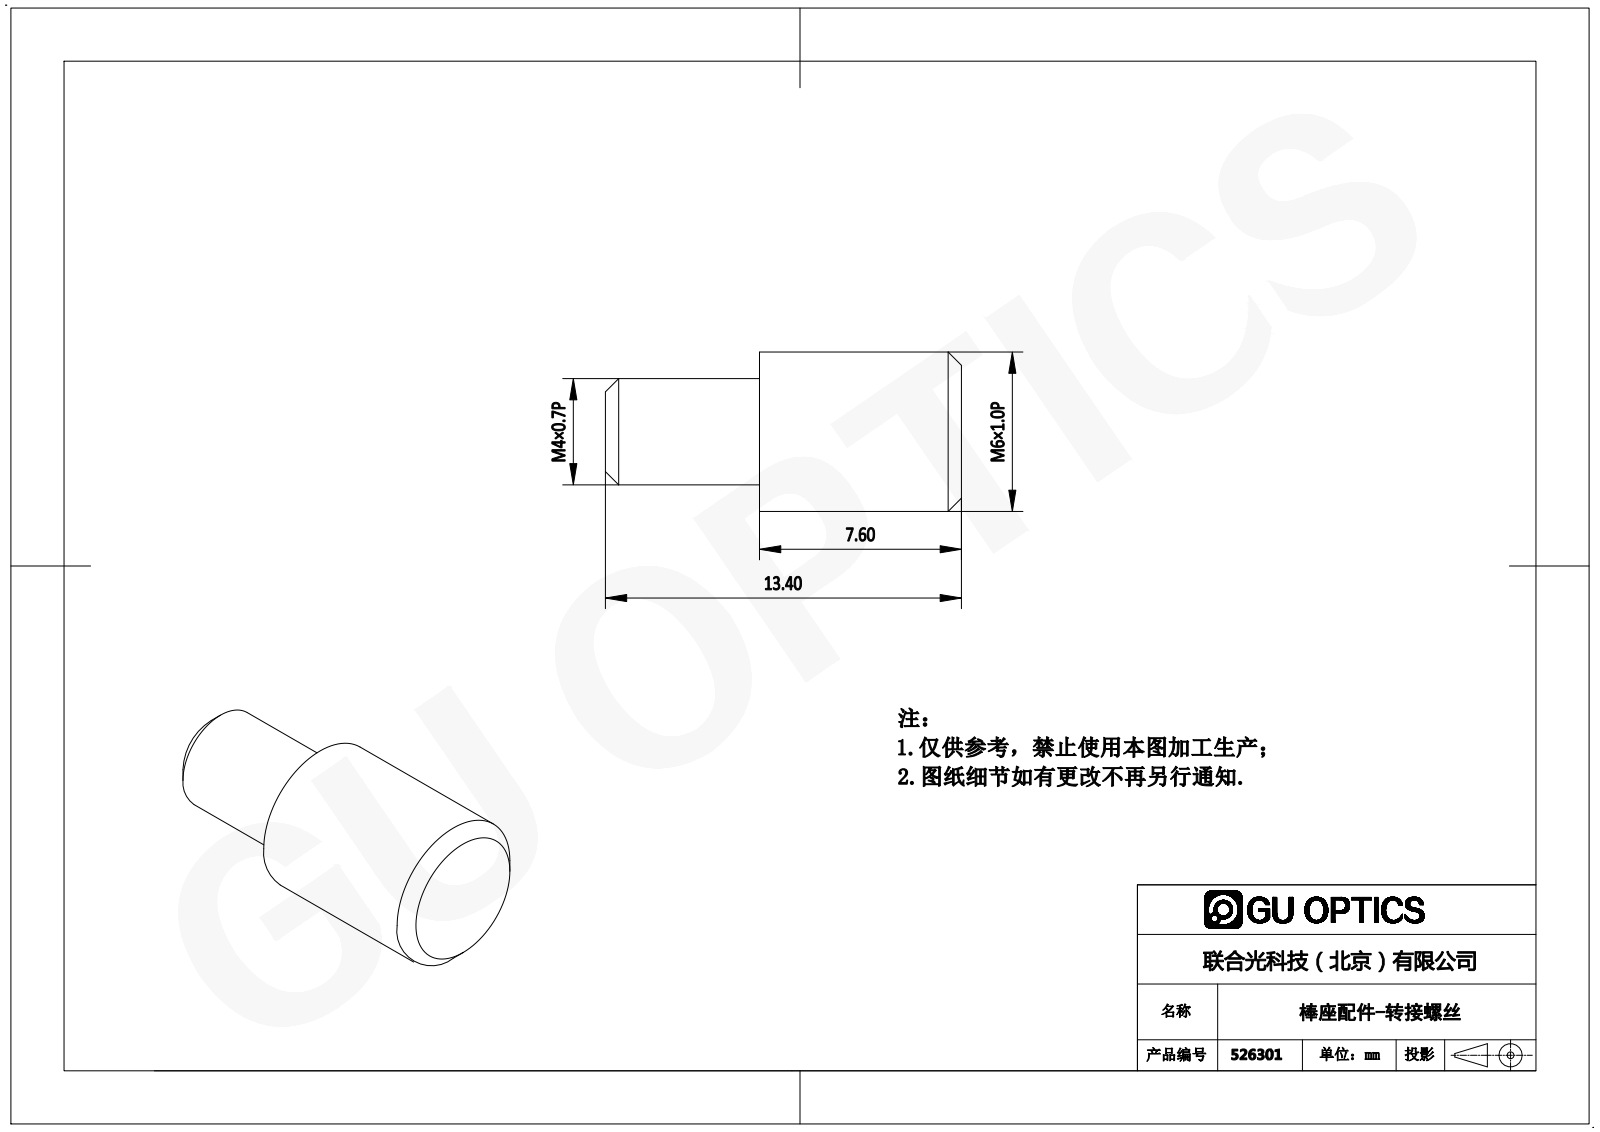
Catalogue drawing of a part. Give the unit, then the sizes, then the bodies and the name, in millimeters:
Units: millimetres
Overall size (bounding box): 13.4 × 6 × 6
Round bosses / shafts (diameter × count): ⌀6 ×1, ⌀4 ×1
Main face-to-face distances: 7.6, 5.8, 13.4
Volume: 284 mm³ · Surface area: 263 mm²
Bodies: 1 solid, 11 faces (3 planar, 4 cylindrical, 4 other)
Part name (STEP PRODUCT): TAE-M4M6
STEP written by: SolidWorks 2019 (CONFIG_CONTROL_DESIGN)
